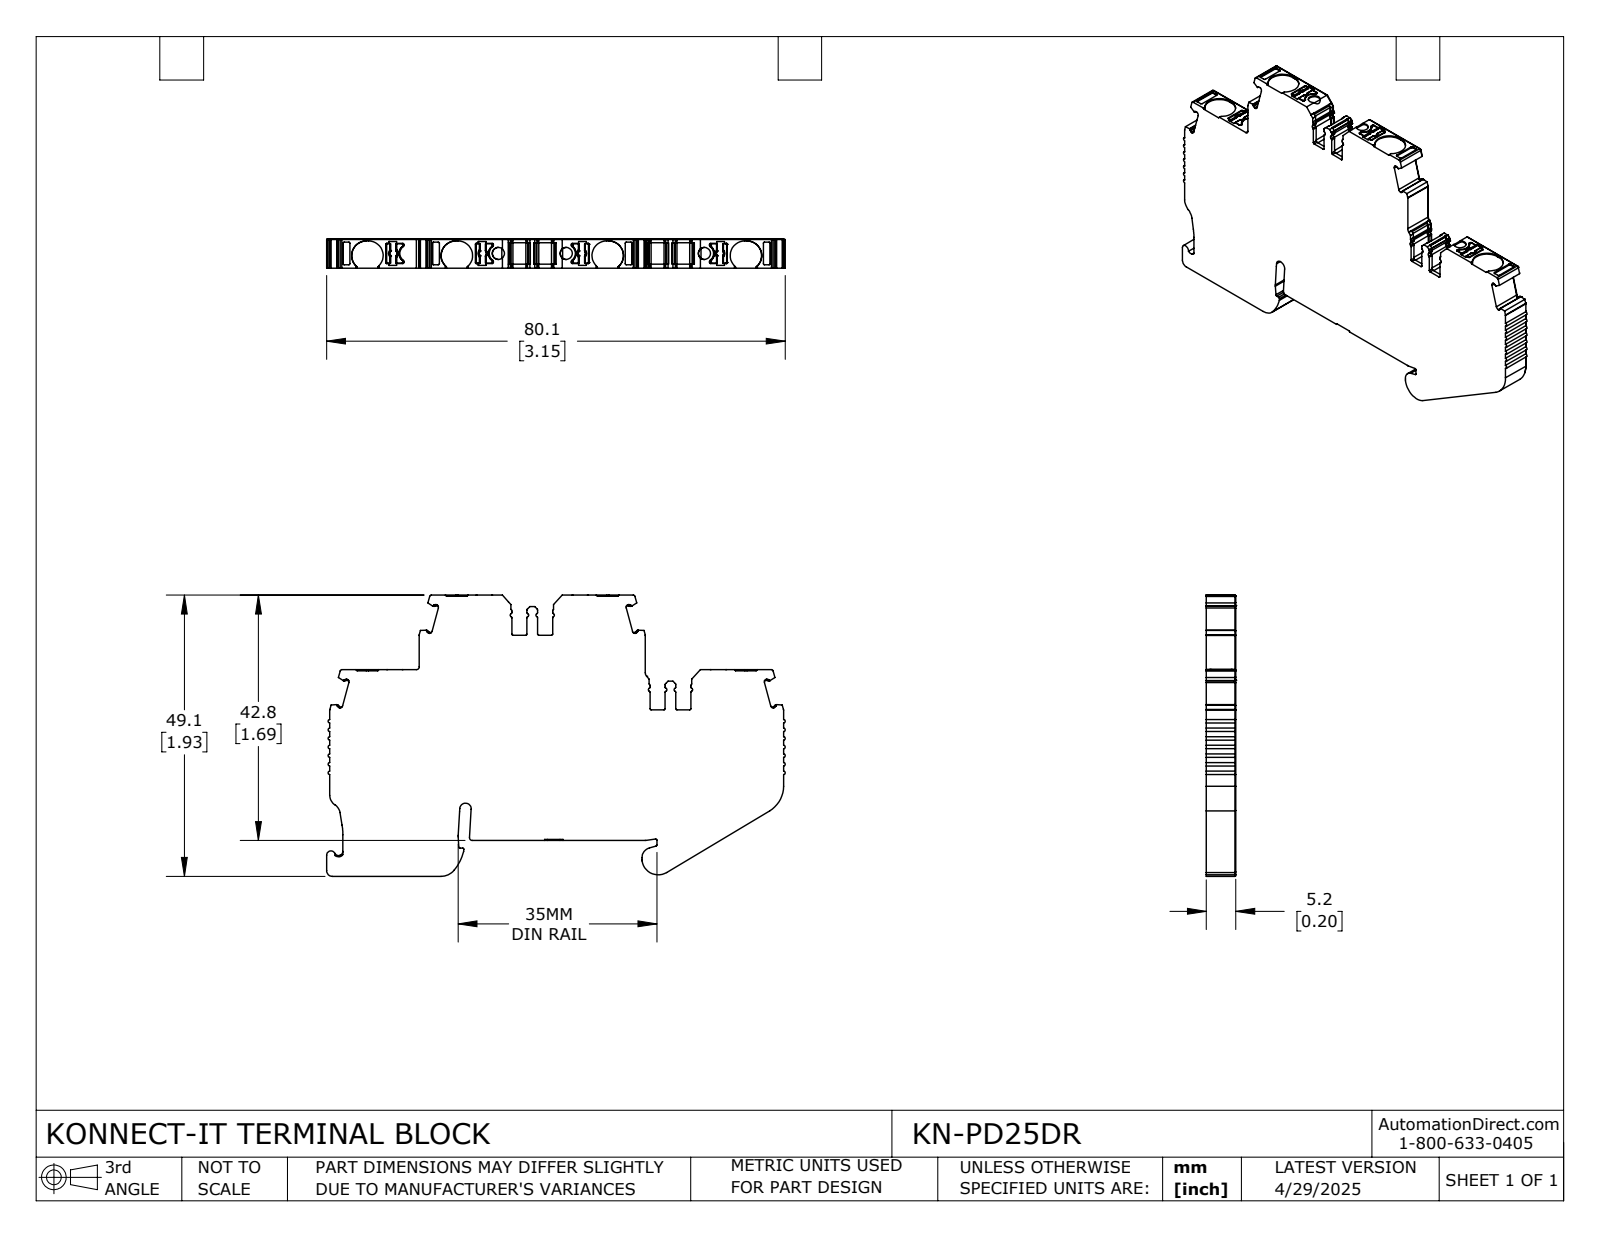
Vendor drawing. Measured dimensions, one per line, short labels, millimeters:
name: KN-PD25DR
written by: SolidWorks 2024 (CONFIG_CONTROL_DESIGN)
unit: mm
bodies: 1 solid, 979 faces (470 planar, 438 cylindrical, 71 other)
size: 80.1 × 49.1 × 5.2
volume: 14 600 mm³; area: 7 503 mm²
holes: 3× ⌀2.1
rounds: 100× R0.2, 57× R0.3, 41× R0.1, 21× R0.5, 17× R0.4, 16× R0.2, 9× R0.6, 8× R0.2
face distances: 5.2, 13, 6.2, 42.6, 29.6, 48.9, 2, 35.9, 12.8, 24.1
hole spacings: 11.8, 24.1, 36
